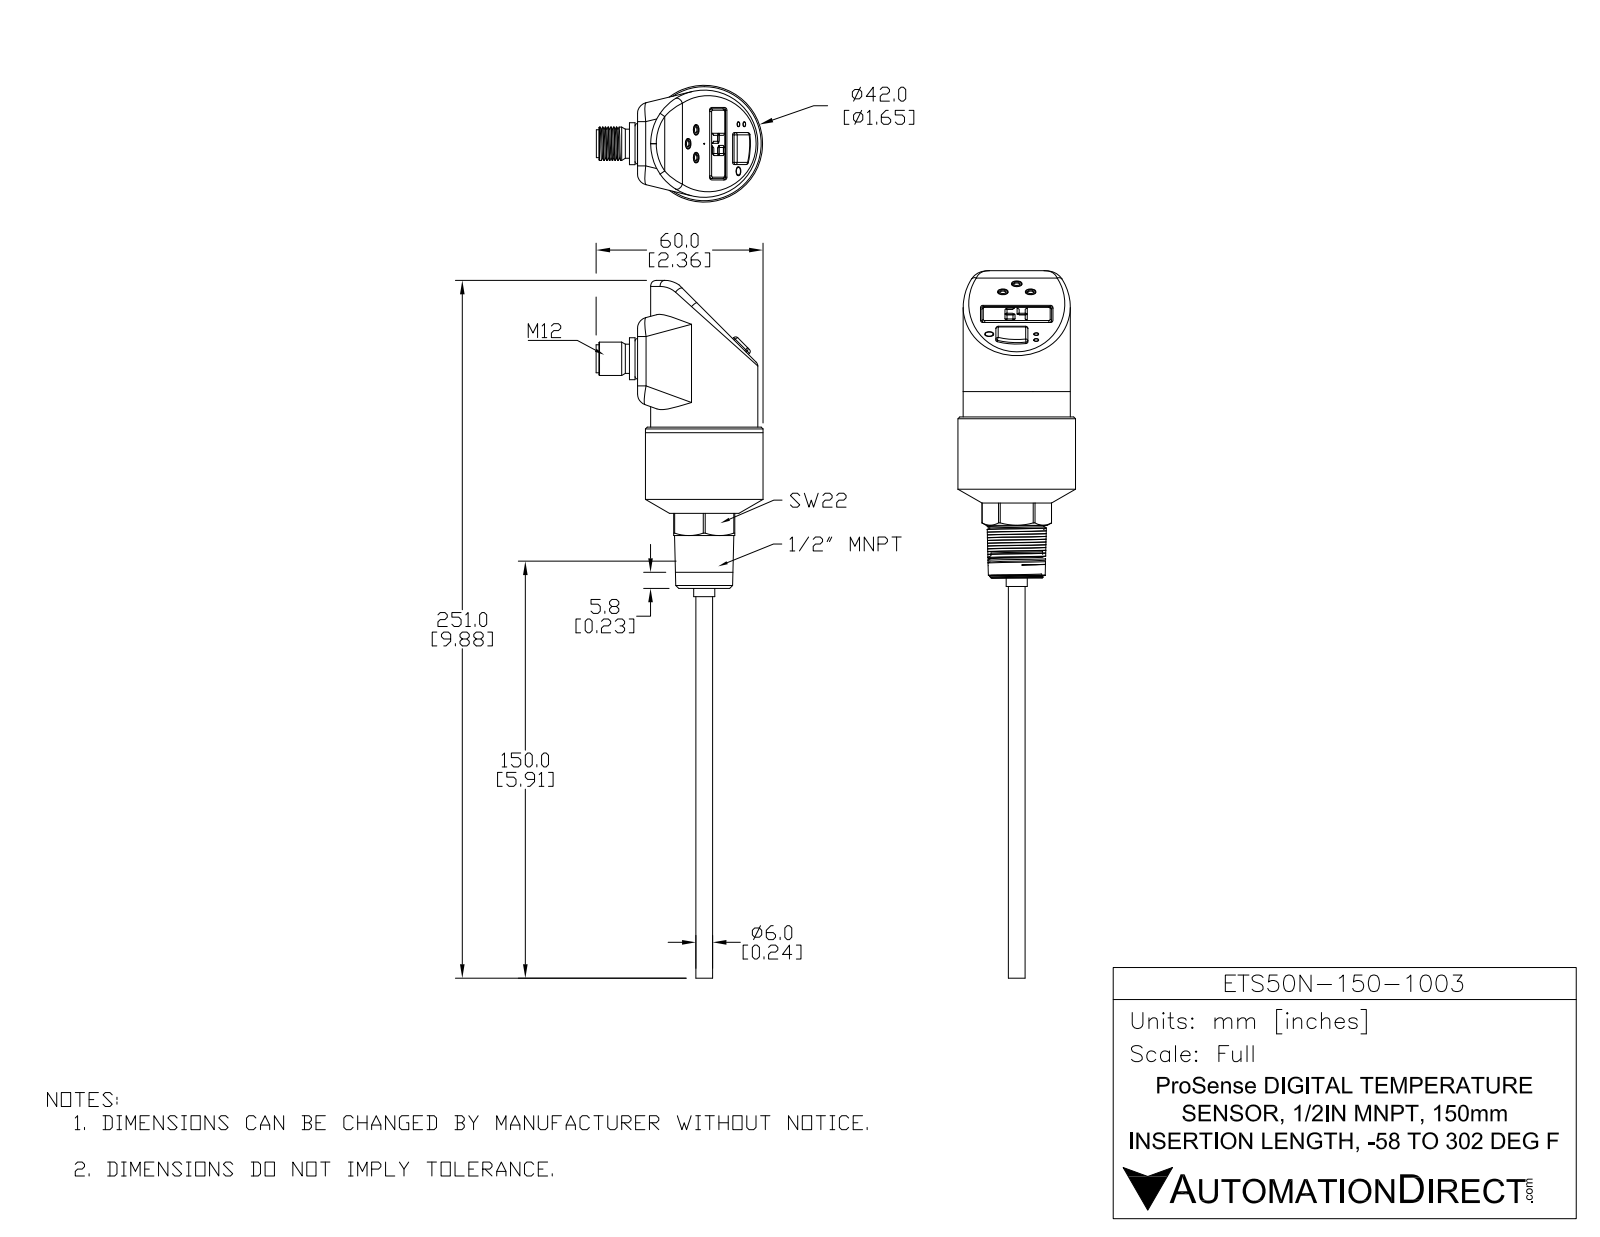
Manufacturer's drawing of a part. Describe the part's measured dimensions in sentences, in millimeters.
The part is named "ETS50N-150-1003". Its 3-D file was written by "SolidWorks 2016 (AUTOMOTIVE_DESIGN)". It is 1 solid with 324 faces: 138 planar, 95 cylindrical and 91 other. Overall it measures 254.49 by 59.95 by 42.3 millimeters. Its volume is 110 571 cubic millimeters and its surface area 20 604 square millimeters. Round holes: 1 of diameter 8.45, 1 of diameter 11. Round bosses or shafts: 4 of diameter 1.4, 4 of diameter 1, 1 of diameter 42.3, 1 of diameter 38.55, 1 of diameter 15.1, 1 of diameter 14.56, 1 of diameter 12, 1 of diameter 10.5. Partial cylindrical surfaces (rounded edges, fillets, slot ends): 8 of radius 1, 7 of radius 0.8, 4 of radius 0.5, 4 of radius 3.99, 4 of radius 7, 1 of radius 0.61, 1 of radius 2, 1 of radius 9.01. The main face-to-face distances are 22, 57.99, 13.9, 13, 0.9, 2, 2.9, 15.9, 37.9, 35.
